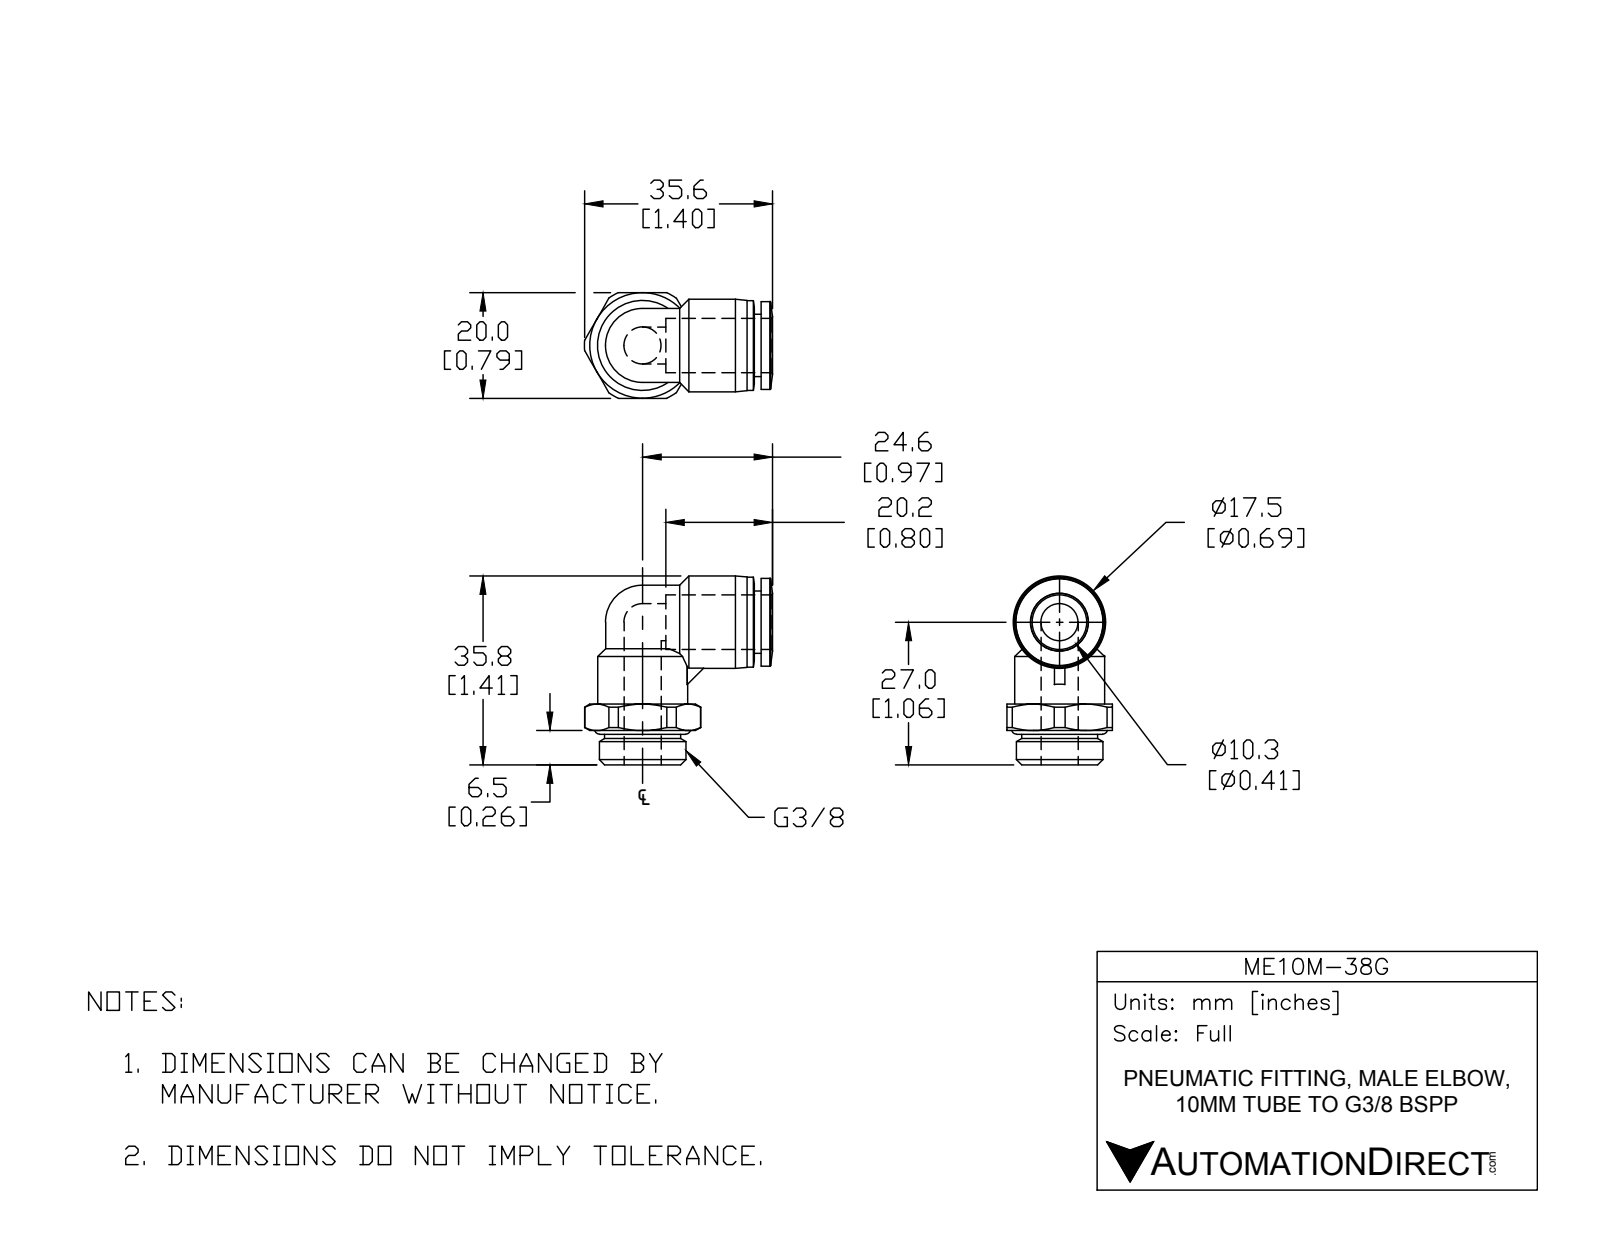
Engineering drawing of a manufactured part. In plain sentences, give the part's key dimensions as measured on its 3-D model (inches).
The part is named "ME10M-38G". Its 3-D file was written by "SolidWorks 2018 (AUTOMOTIVE_DESIGN)". It is 2 solids with 87 faces: 18 planar, 30 cylindrical and 39 other. Overall it measures 1.407 by 1.402 by 0.787 inches. Its volume is 0.493 cubic inches and its surface area 8.032 square inches. Round holes: 2 of diameter 0.276, 1 of diameter 0.406. Round bosses or shafts: 2 of diameter 0.669, 1 of diameter 0.689, 1 of diameter 0.654, 1 of diameter 0.646, 1 of diameter 0.567, 1 of diameter 0.551, 1 of diameter 0.465. Partial cylindrical surfaces (rounded edges, fillets, slot ends): 1 of radius 0.276, 1 of radius 0.433. The main face-to-face distances are 0.787, 0.453, 0.049, 0.659, 0.709, 0.256, 0.197, 0.303, 0.047, 0.15.
